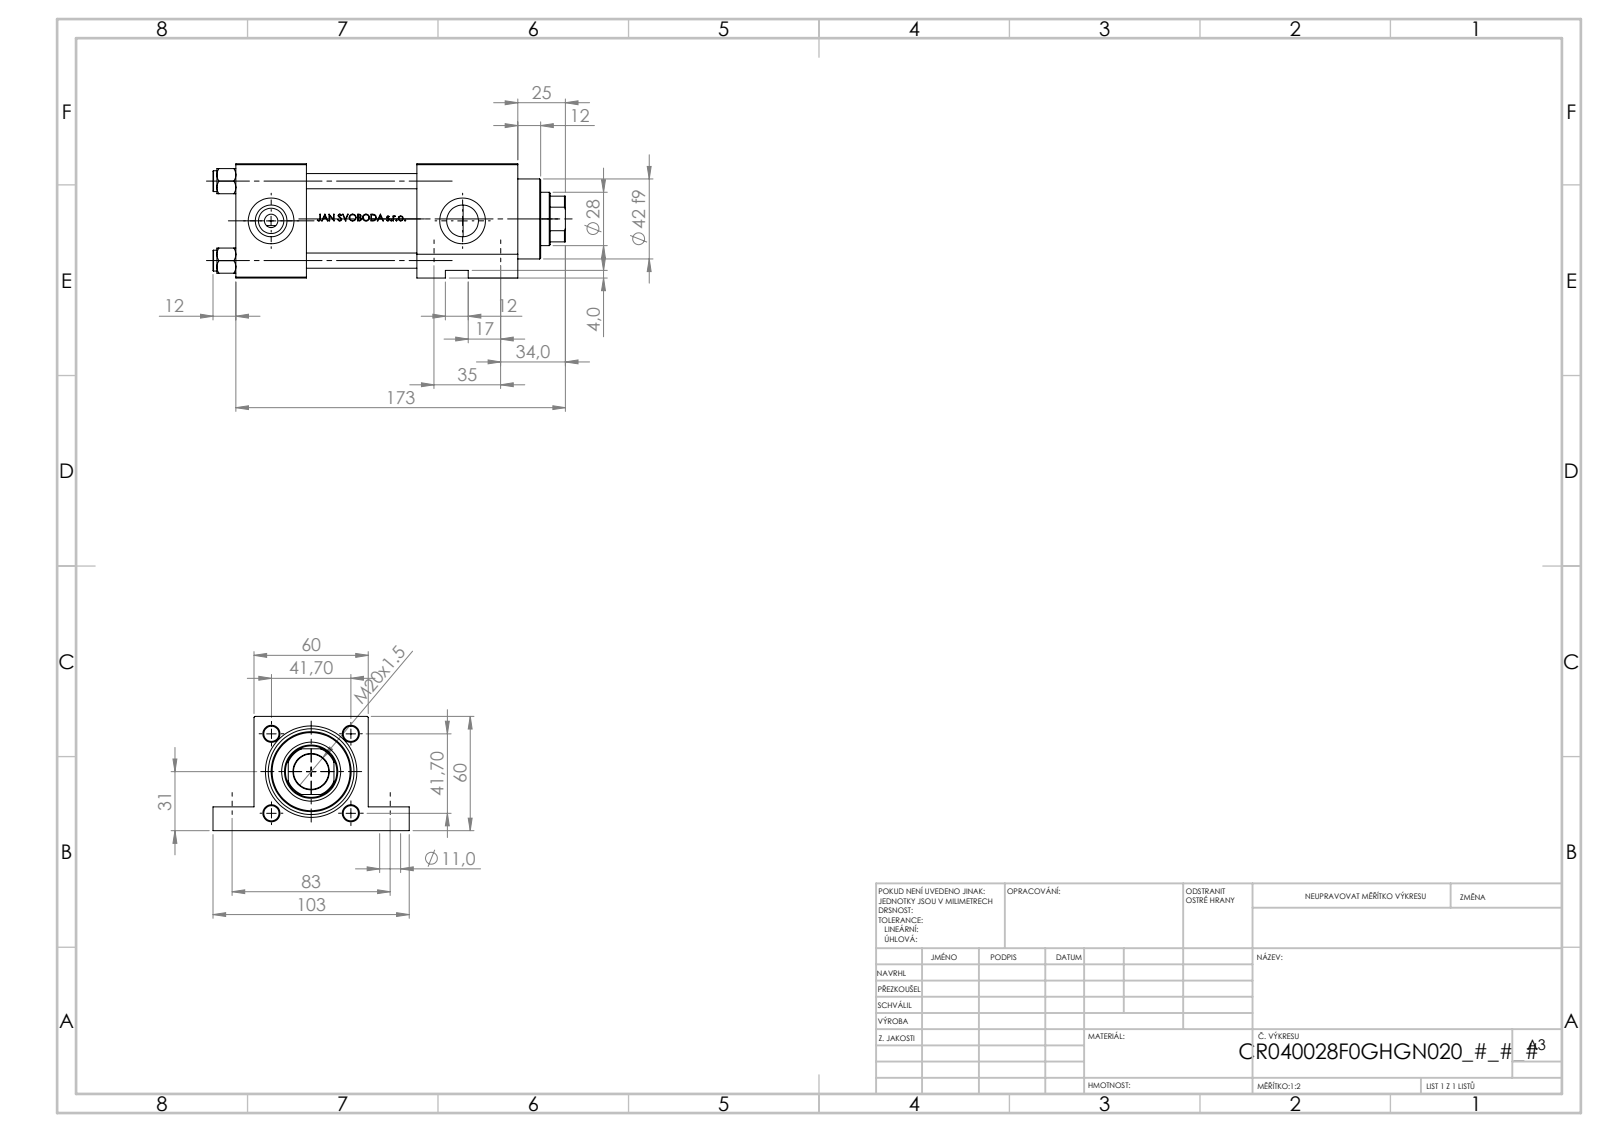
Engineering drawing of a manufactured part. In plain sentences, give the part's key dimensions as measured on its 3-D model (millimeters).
The part is named "V215CR_F_Body; NUT_M5_F; V215CR_VCP_F; V215CR_F_TYCINKA (+1 more)". Its 3-D file was written by "SolidWorks 2019 (CONFIG_CONTROL_DESIGN)". It is 11 solids with 1118 faces: 437 planar, 141 cylindrical and 540 other. Overall it measures 185 by 103 by 60 millimeters. Its volume is 445 246 cubic millimeters and its surface area 117 639 square millimeters. Round holes: 4 of diameter 8, 2 of diameter 7, 2 of diameter 11, 2 of diameter 11, 2 of diameter 16.66, 2 of diameter 24, 1 of diameter 18.5, 1 of diameter 28, 1 of diameter 31, 1 of diameter 40, 1 of diameter 45. Round bosses or shafts: 4 of diameter 11, 1 of diameter 46, 1 of diameter 42. Partial cylindrical surfaces (rounded edges, fillets, slot ends): 1 of radius 13.5. The main face-to-face distances are 60, 37, 95, 58, 148, 111, 53, 12.5, 47.5, 38. The hole center spacings are 41.7, 28.79, 30.2, 35, 58.97, 83, 90.08, 100.5.
